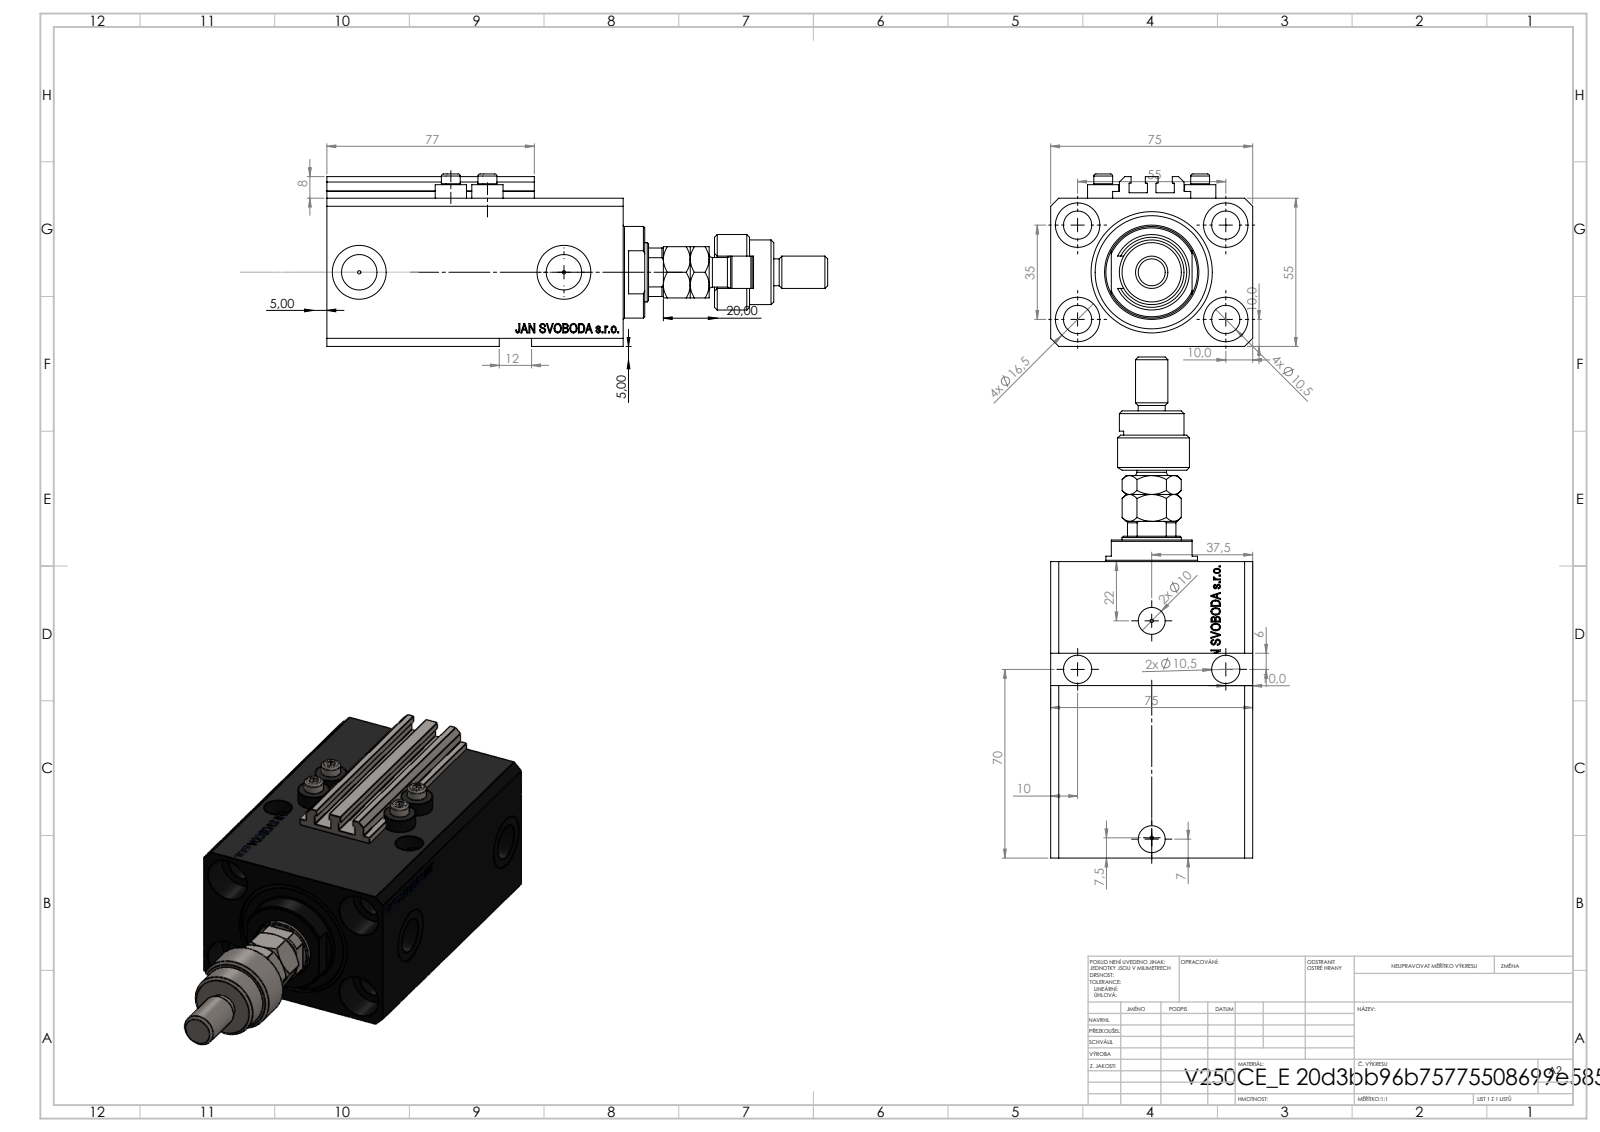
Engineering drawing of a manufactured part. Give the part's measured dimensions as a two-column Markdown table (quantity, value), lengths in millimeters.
| quantity | value |
| --- | --- |
| part name | FEMALE_PART_FOR_DFA; ALLEN BOLT V250CE; V250CE_E_Body; V250CE_VC_E (+2 more) |
| STEP written by | SolidWorks 2019 (CONFIG_CONTROL_DESIGN) |
| units | millimeters |
| bodies | 10 solids, 1185 faces (546 planar, 171 cylindrical, 468 other) |
| overall size | 186 × 75 × 64 |
| volume | 395 598 mm³ |
| surface area | 103 912 mm² |
| round holes (diameter × count) | 10.5 × 9, 1.25 × 4, 4 × 4, 16.5 × 4, 10 × 2, 13.16 × 2, 20 × 2, 22 × 1, 32 × 1, 45 × 1 |
| round bosses / shafts (diameter × count) | 11.6 × 4, 7 × 4, 34 × 1, 28 × 1, 24 × 1, 18 × 1, 12 × 1, 11 × 1 |
| partial cylindrical surfaces (radius × count) | 0.2 × 10, 9.75 × 1, 10.5 × 1 |
| main face-to-face distances | 55, 75, 15, 110, 95, 9.9, 3, 8, 19, 85.1 |
| hole center spacings | 32.6, 32.87, 55, 68.74, 13.6, 14.09, 23.05, 25.81 |
